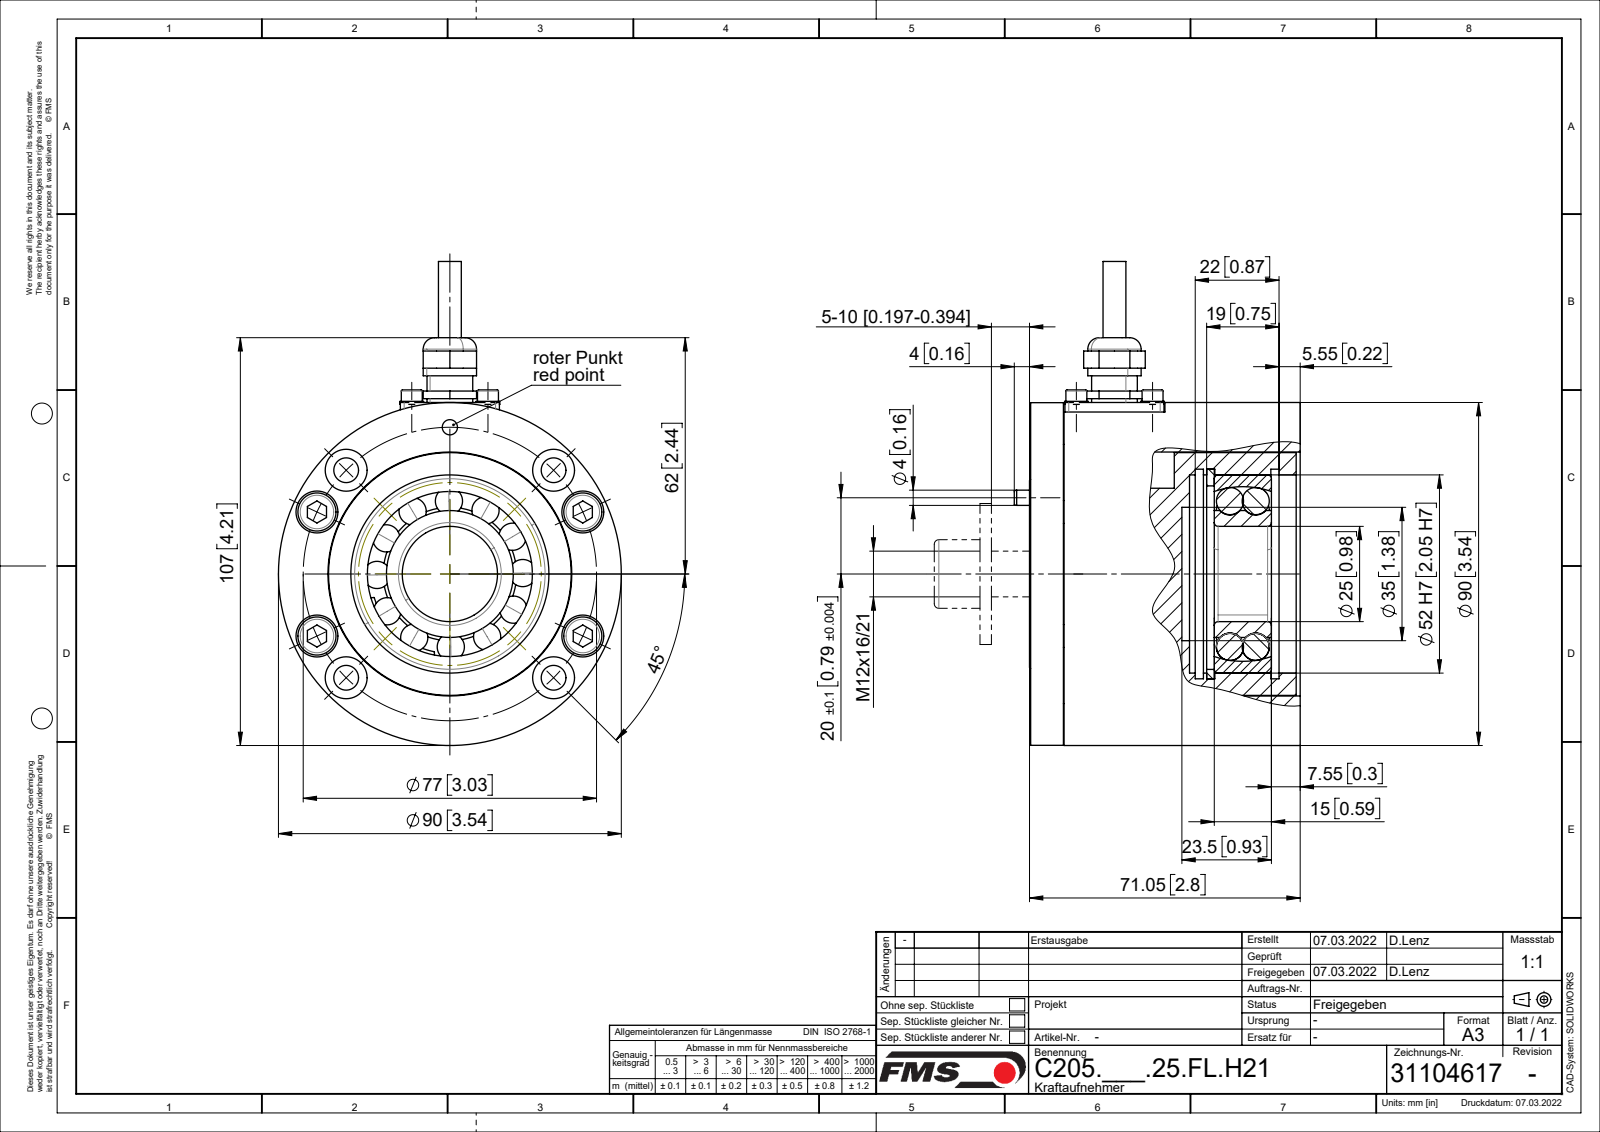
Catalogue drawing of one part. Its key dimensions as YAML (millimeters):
part_name: "PKL_1205_01; Federringe_DIN127A_M03; Zyl-Schr DIN912_M6x30; 31104488_01 (+8 more)"
step_written_by: "SolidWorks 2018 (CONFIG_CONTROL_DESIGN)"
units: millimeters
bodies: {solids: 48, faces: 577, planar: 201, cylindrical: 230, other: 146}
overall_size: [127, 96.05, 90]
volume: 310171
surface_area: 122941
round_holes:
  - {diameter: 6.5, count: 8}
  - {diameter: 11, count: 8}
  - {diameter: 2.5, count: 6}
  - {diameter: 3.1, count: 4}
  - {diameter: 3.4, count: 4}
  - {diameter: 5, count: 4}
  - {diameter: 7, count: 4}
  - {diameter: 4, count: 2}
  - {diameter: 3, count: 1}
  - {diameter: 6, count: 1}
  - {diameter: 10.2, count: 1}
  - {diameter: 12.2, count: 1}
round_bosses_or_shafts:
  - {diameter: 10, count: 4}
  - {diameter: 6.2, count: 4}
  - {diameter: 6, count: 4}
  - {diameter: 5.5, count: 4}
  - {diameter: 3, count: 4}
  - {diameter: 12, count: 2}
  - {diameter: 90, count: 1}
  - {diameter: 89.9, count: 1}
partial_cylinders:
  - {radius: 0.1, count: 4}
  - {radius: 1, count: 4}
  - {radius: 0.5, count: 2}
  - {radius: 4.24, count: 2}
  - {radius: 5, count: 2}
  - {radius: 20.8, count: 1}
  - {radius: 24.1, count: 1}
face_to_face_distances: [6, 6.5, 32, 25.5, 2, 33.05, 38, 8.6, 29.1, 37.7]
hole_center_spacings: [20, 38.5, 13.37, 14.14, 38.49, 44.16, 54.44, 63.07]
